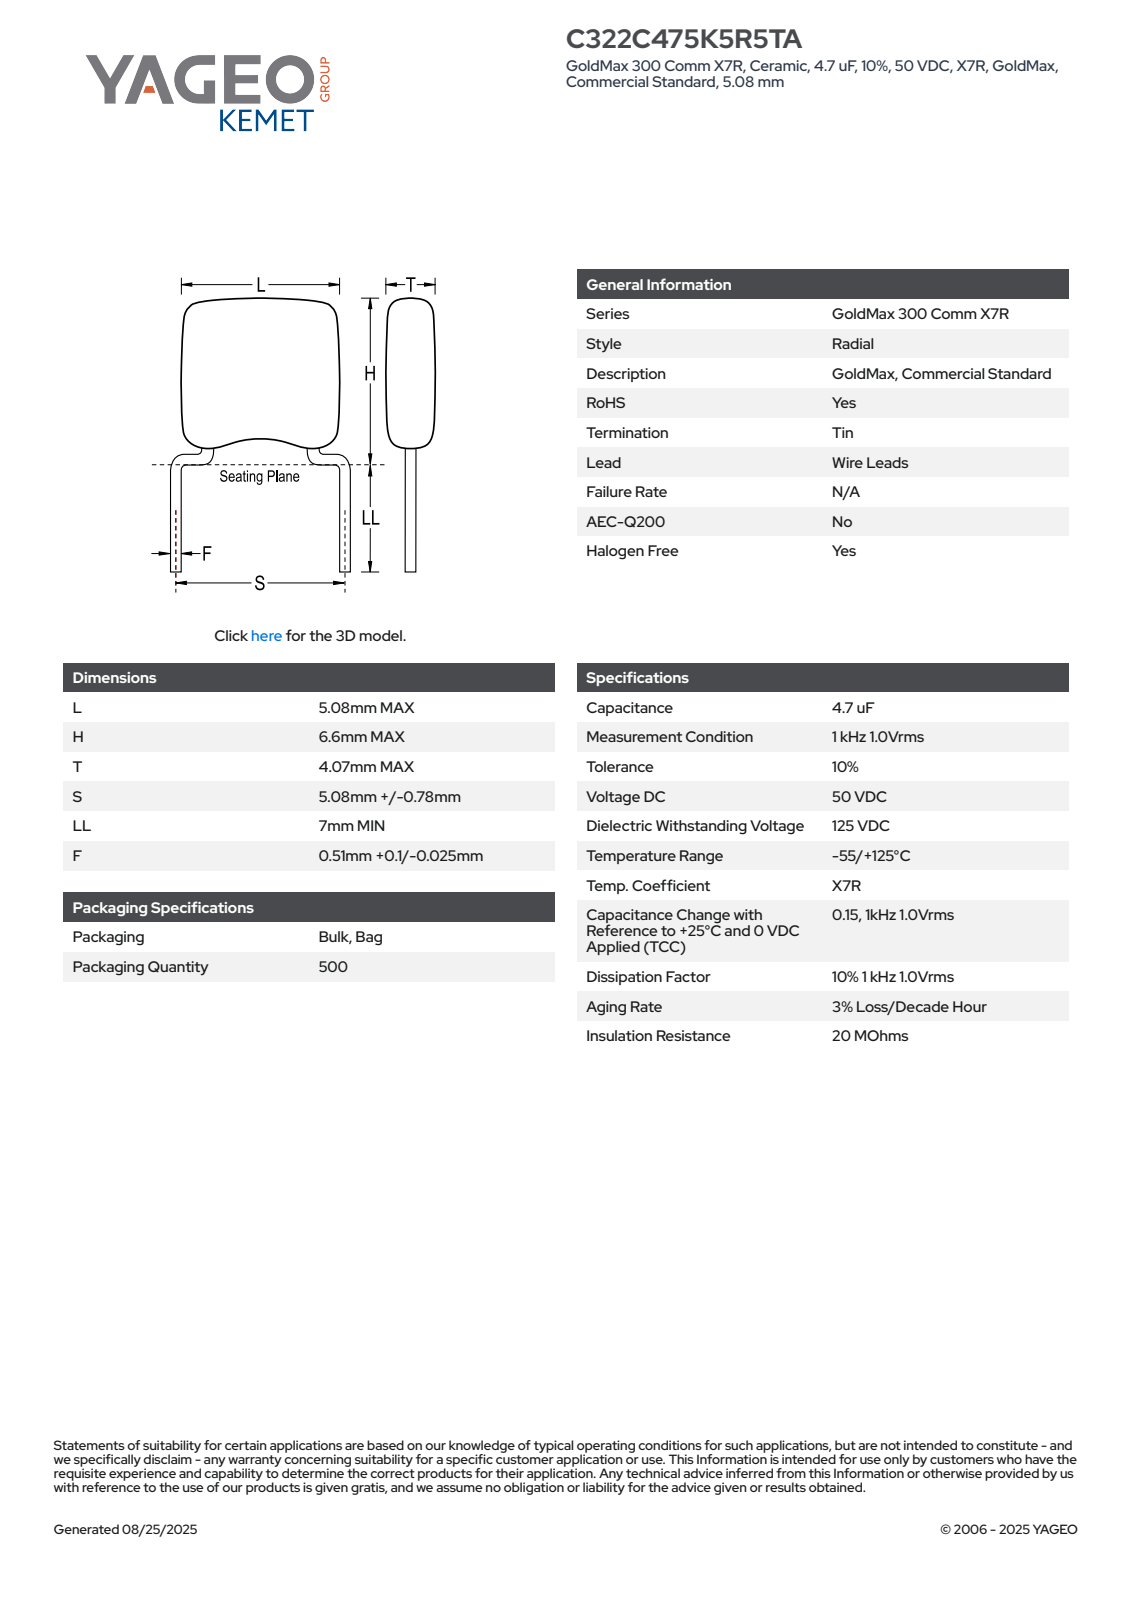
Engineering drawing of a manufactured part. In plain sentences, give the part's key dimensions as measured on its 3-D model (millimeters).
The part is named "CCR_SB_5.08X6.6_L5.08H6.6T4.07S5.08LL7F0.51". Its 3-D file was written by "SolidWorks 2014 (AUTOMOTIVE_DESIGN)". It is 4 solids with 97 faces: 65 planar, 14 cylindrical and 18 other. Overall it measures 13.6 by 5.59 by 4.08 millimeters. Its volume is 94 cubic millimeters and its surface area 139 square millimeters. Round bosses or shafts: 2 of diameter 0.51. Partial cylindrical surfaces (rounded edges, fillets, slot ends): 10 of radius 1. The main face-to-face distances are 4.07, 5.08, 4.81, 4.08, 0.43, 2.64, 2.17, 2.21, 2.6, 0.39.
